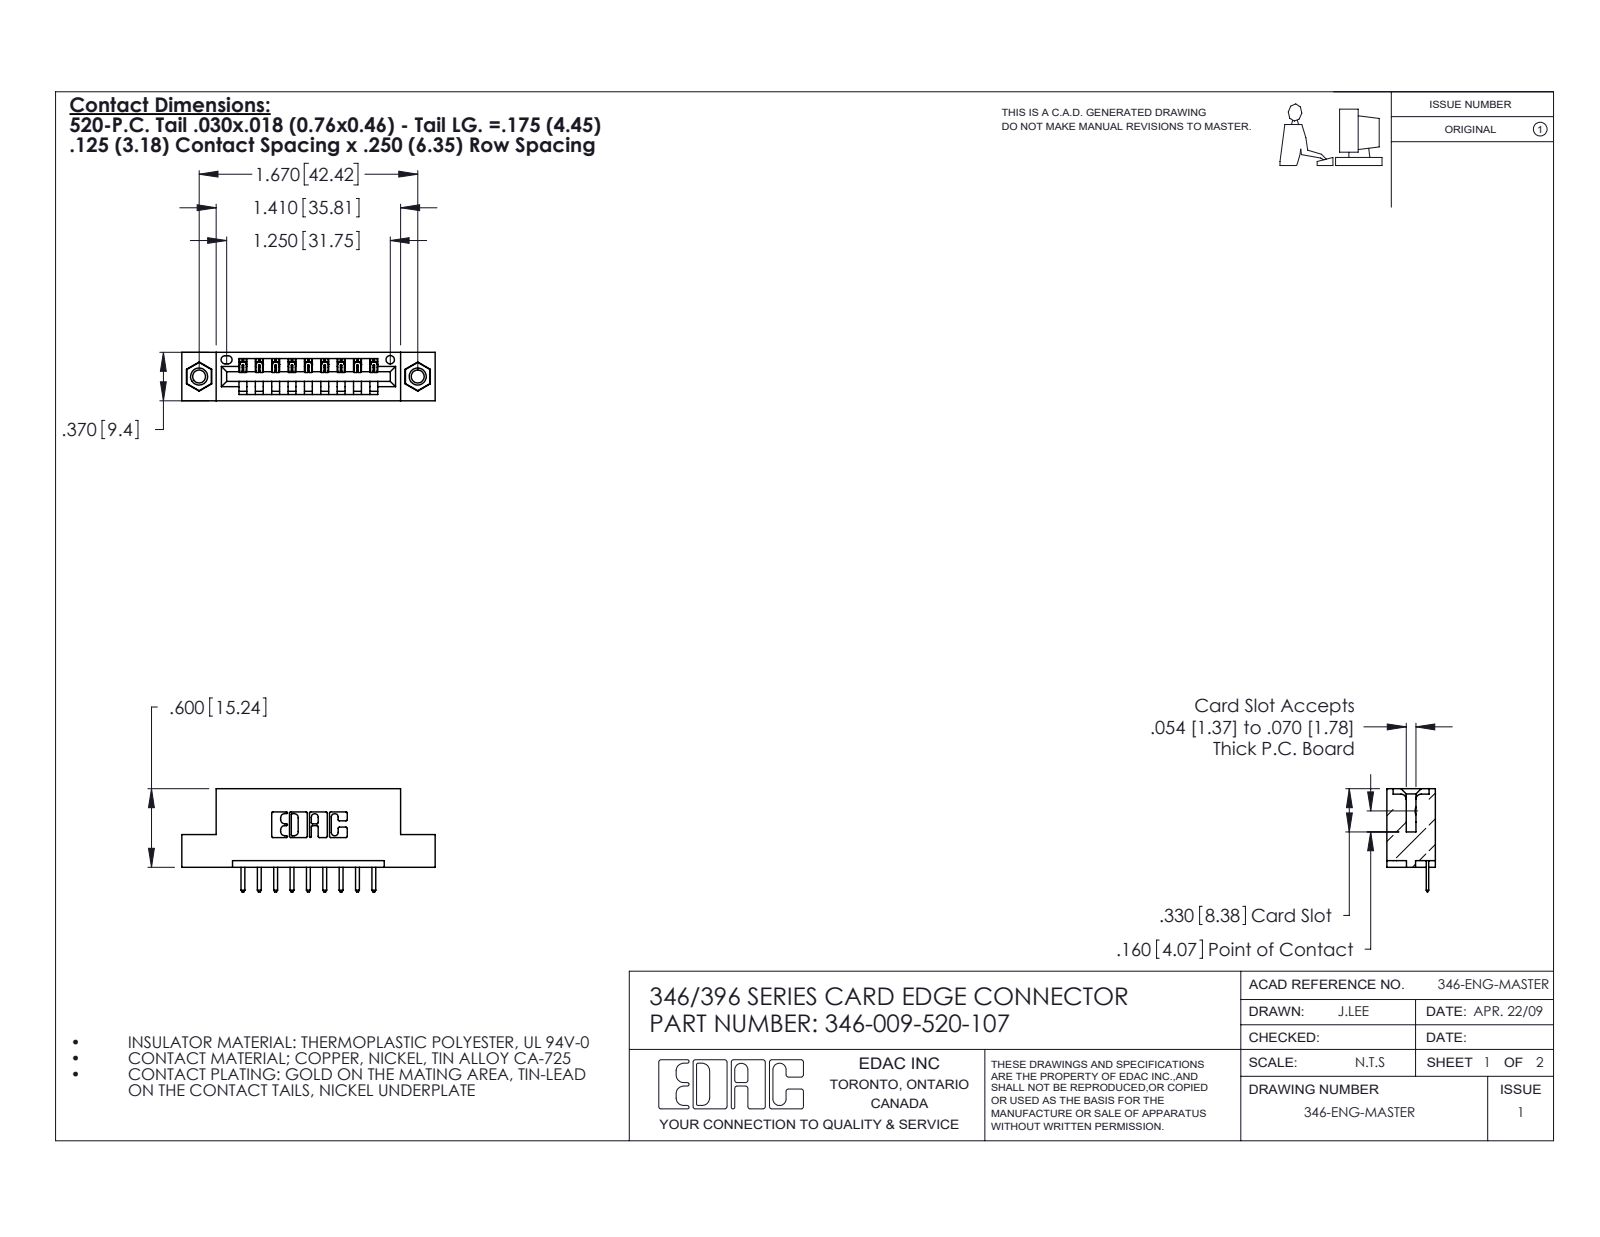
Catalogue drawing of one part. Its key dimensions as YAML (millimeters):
part_name: "345-250-001_345-250-005-103; 346 Part_Flush Mounting Lugs - 0.156 Dia-TI; 346-009-520-107; 345-292-001_345-293-120"
step_written_by: "SolidWorks 2020 (CONFIG_CONTROL_DESIGN)"
units: millimeters
bodies: {solids: 12, faces: 740, planar: 486, cylindrical: 238, other: 16}
overall_size: [49.1, 20, 9.4]
volume: 4440
surface_area: 5139
round_holes:
  - {diameter: 2.5, count: 2}
  - {diameter: 3.2, count: 2}
  - {diameter: 4, count: 2}
  - {diameter: 1.6, count: 1}
round_bosses_or_shafts:
  - {diameter: 3.9, count: 2}
partial_cylinders:
  - {radius: 0.3, count: 22}
  - {radius: 0.3, count: 20}
  - {radius: 0.2, count: 18}
  - {radius: 0.2, count: 6}
  - {radius: 0.8, count: 6}
  - {radius: 0.7, count: 3}
  - {radius: 0.8, count: 2}
  - {radius: 1, count: 2}
face_to_face_distances: [6.4, 9.4, 1.2, 8.2, 3.8, 5.6, 2.5, 4.4, 3.2, 12.7]
hole_center_spacings: [6.2, 37.2, 42.4]
